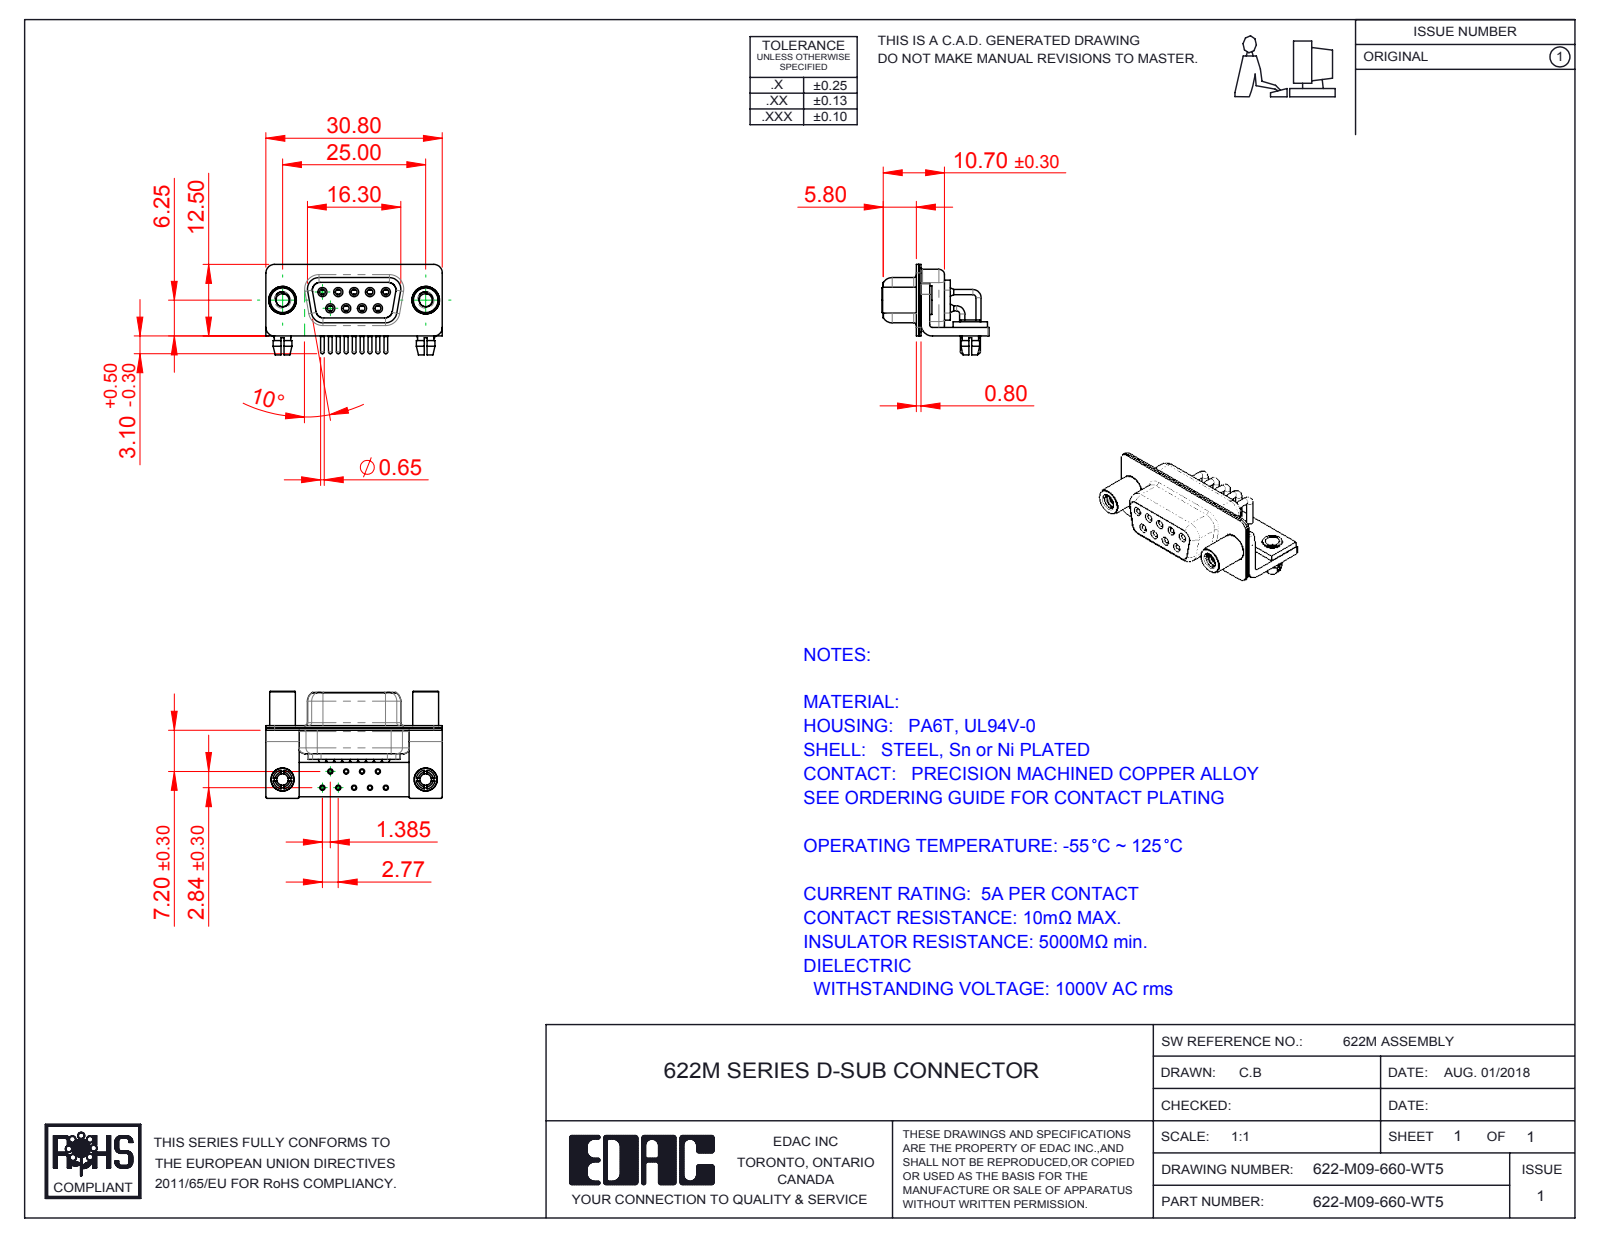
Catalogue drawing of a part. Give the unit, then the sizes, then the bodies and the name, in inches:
Units: inches
Overall size (bounding box): 1.213 × 0.736 × 0.622
Round holes (diameter × count): ⌀0.079 ×11, ⌀0.035 ×9, ⌀0.039 ×9, ⌀0.043 ×9, ⌀0.067 ×9, ⌀0.071 ×9, ⌀0.089 ×2, ⌀0.098 ×2, ⌀0.126 ×2, ⌀0.157 ×2, ⌀0.189 ×2
Round bosses / shafts (diameter × count): ⌀0.063 ×9, ⌀0.059 ×9, ⌀0.035 ×9, ⌀0.026 ×9, ⌀0.197 ×2, ⌀0.193 ×2, ⌀0.177 ×2, ⌀0.157 ×2
Partial cylindrical surfaces — rounded edges, fillets, slot ends (radius × count): R0.01 ×16, R0.059 ×16, R0.079 ×13, R0.053 ×8, R0.063 ×8, R0.02 ×5, R0.024 ×4, R0.026 ×4
Main face-to-face distances: 0.016, 0.031, 0.091, 0.059, 0.075, 0.039, 0.368, 0.057, 0.335, 0.352
Hole centre spacings: 0.124, 0.109, 0.218, 0.198, 0.198, 0.327, 0.294, 0.295
Volume: 0.141 in³ · Surface area: 9.43 in²
Bodies: 19 solids, 966 faces (278 planar, 458 cylindrical, 230 other)
Part name (STEP PRODUCT): 622M Shell Front_09 Contacts; 622M Housing_09 Contacts; 622-M09-660-WT5; 622M Board Lock (+6 more)
STEP written by: SolidWorks 2016 (CONFIG_CONTROL_DESIGN)
